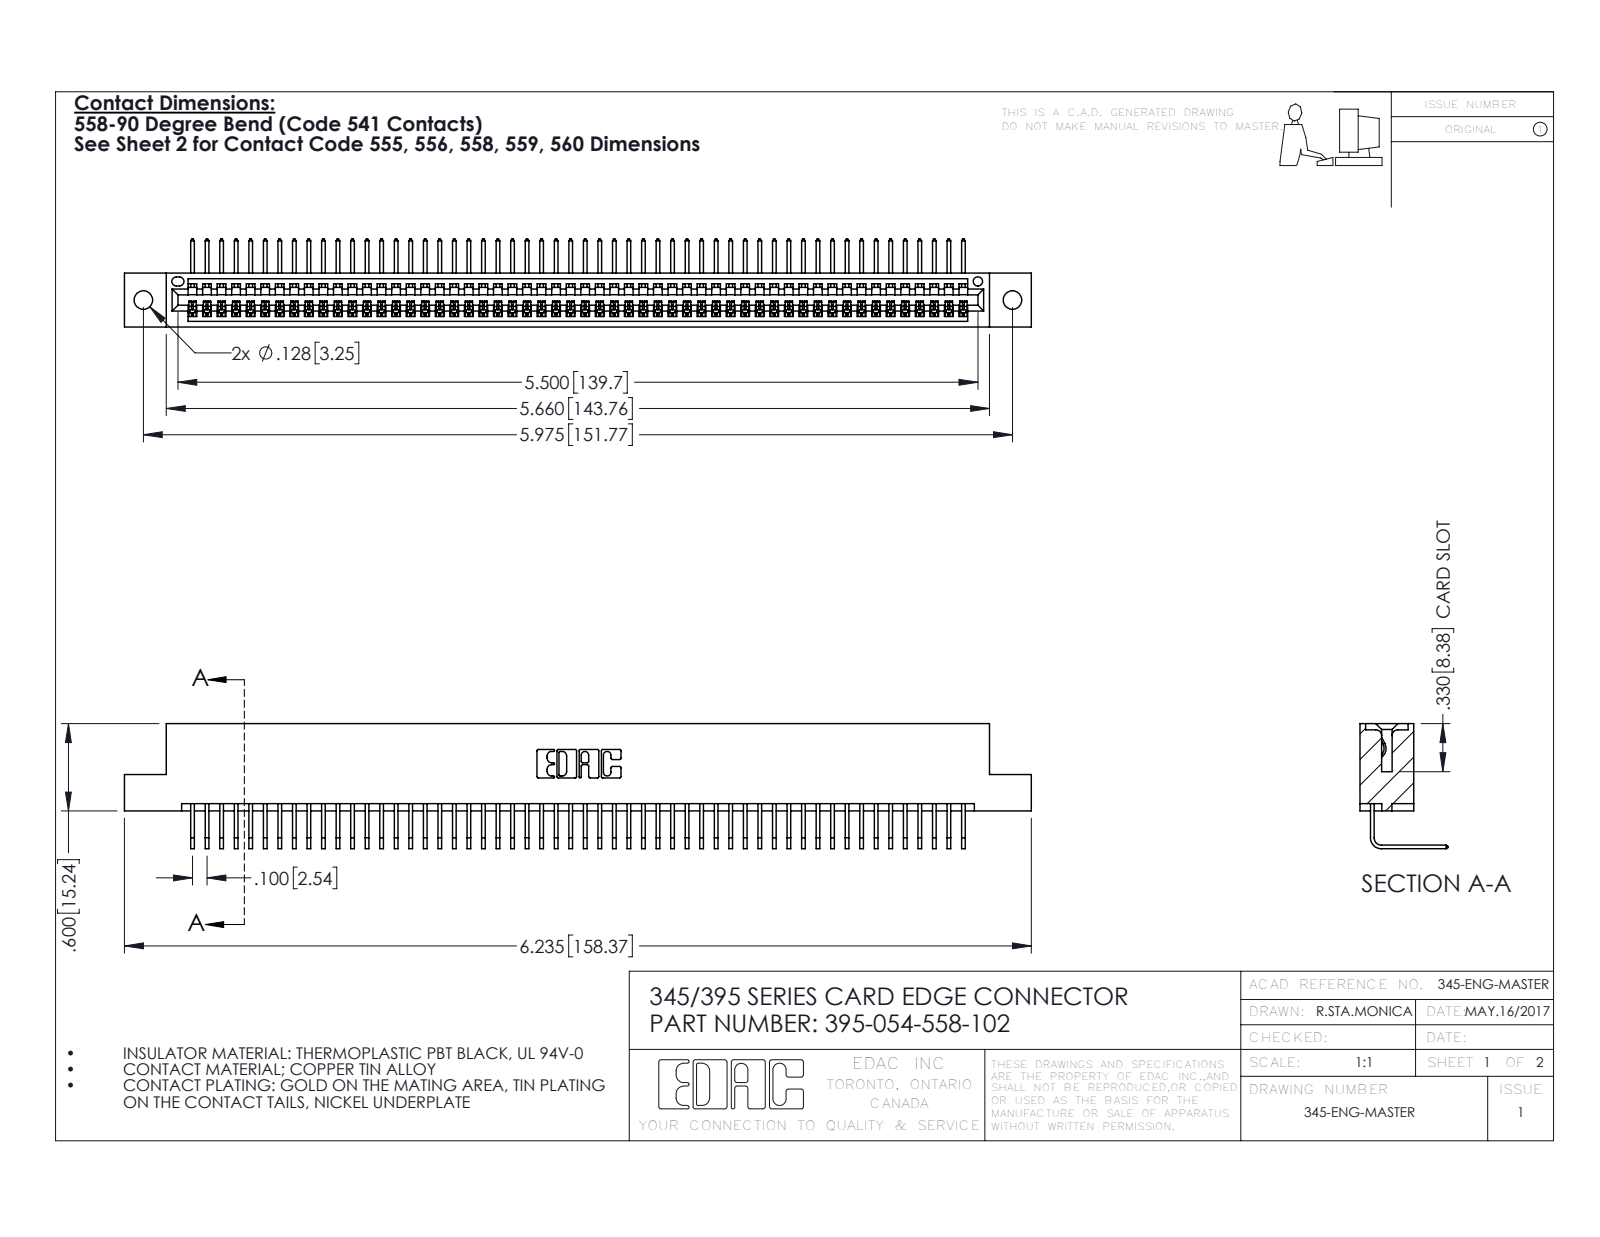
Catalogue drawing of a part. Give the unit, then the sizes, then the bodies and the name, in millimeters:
Units: millimetres
Overall size (bounding box): 158.4 × 21.8 × 15.4
Round holes (diameter × count): ⌀3.3 ×2, ⌀1.6 ×1
Partial cylindrical surfaces — rounded edges, fillets, slot ends (radius × count): R0.2 ×108, R0.3 ×22, R0.2 ×6, R0.8 ×6, R0.7 ×3, R0.8 ×2, R1 ×2, R0.4 ×1
Main face-to-face distances: 7.6, 1.8, 9.4, 5.1, 2.5, 6.9, 0.6, 5.7, 3.8, 1.8
Hole centre spacings: 6.9, 145.8, 151.8
Volume: 15 300 mm³ · Surface area: 21 260 mm²
Bodies: 55 solids, 3366 faces (2348 planar, 1018 cylindrical, 0 other)
Part name (STEP PRODUCT): 345 Part_Flush Mounting Lugs - 0.128 Dia; 345-292-001_558 Tail - 2; 395-054-558-102
STEP written by: SolidWorks 2016 (CONFIG_CONTROL_DESIGN)
